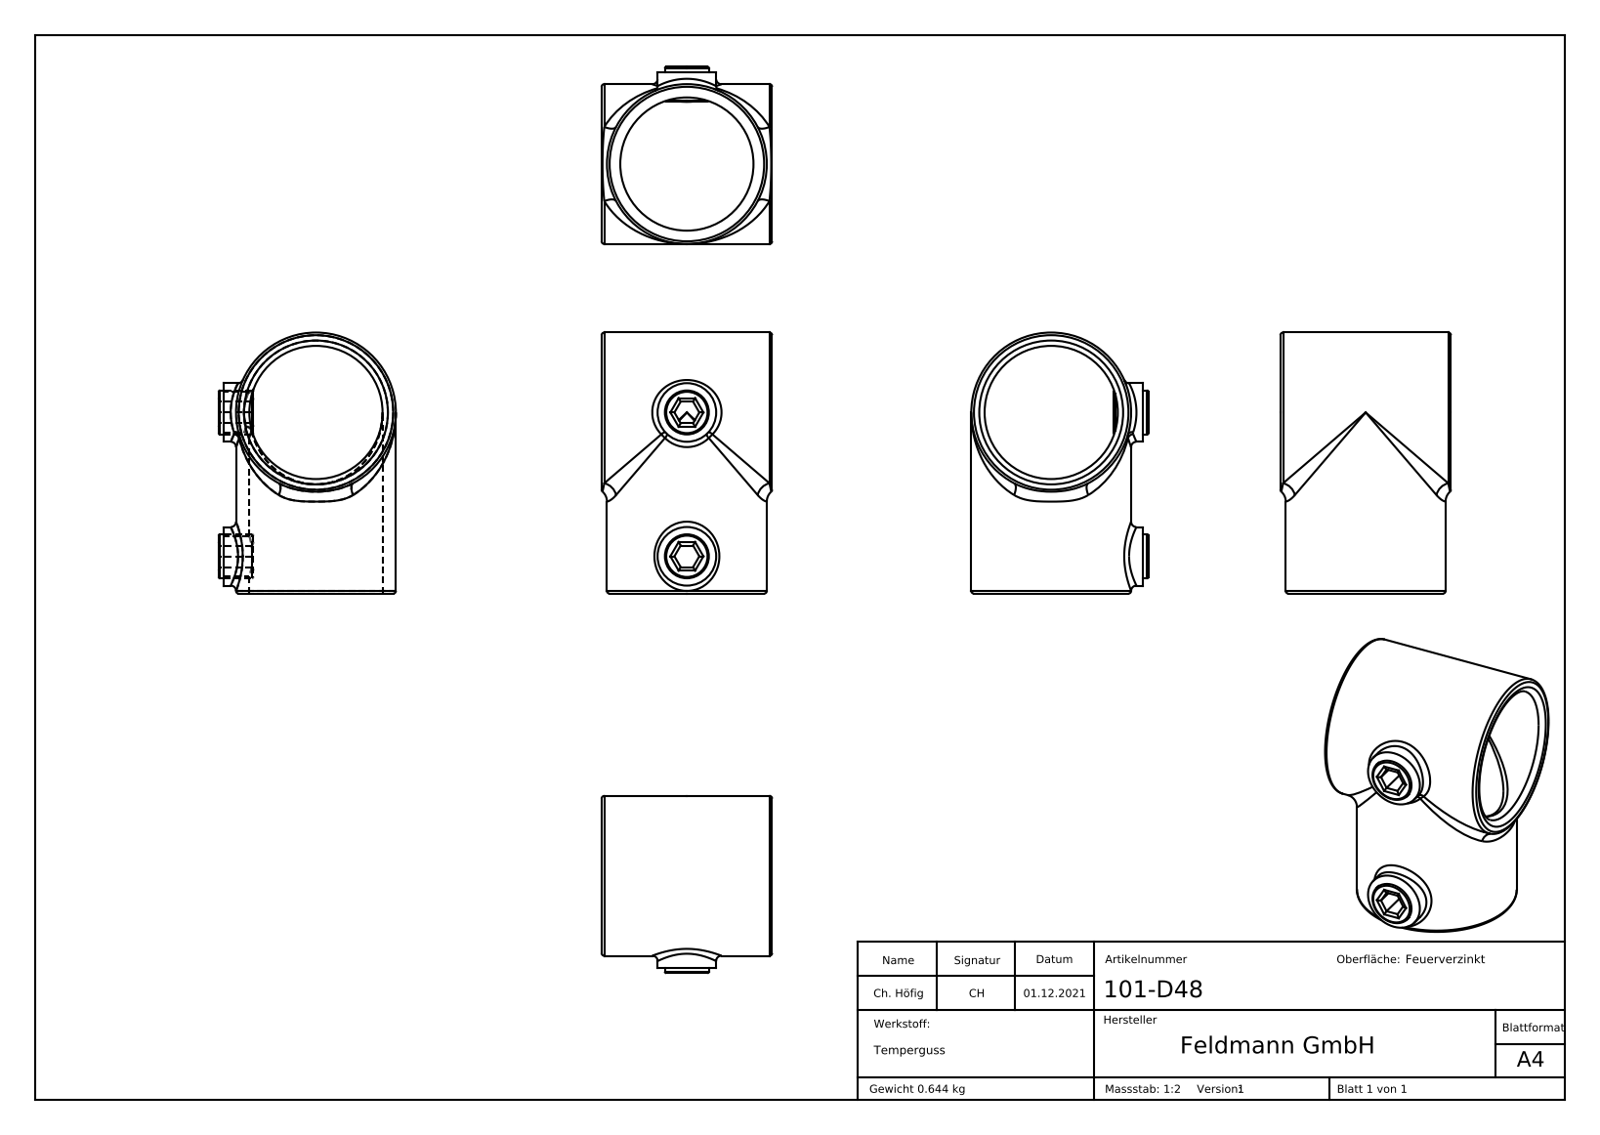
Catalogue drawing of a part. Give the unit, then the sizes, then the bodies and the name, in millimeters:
Units: millimetres
Overall size (bounding box): 98 × 66.5 × 64
Round holes (diameter × count): ⌀15.25 ×2, ⌀50 ×2
Round bosses / shafts (diameter × count): ⌀60 ×2, ⌀22 ×2, ⌀16.5 ×2
Partial cylindrical surfaces — rounded edges, fillets, slot ends (radius × count): R2 ×24
Main face-to-face distances: 64, 27, 8.1, 11, 13, 2, 54, 8.09, 9.95, 63.95
Hole centre spacings: 54
Volume: 87 830 mm³ · Surface area: 38 792 mm²
Bodies: 3 solids, 81 faces (21 planar, 34 cylindrical, 26 other)
Part name (STEP PRODUCT): 101-D48 Teil2; 101-D48 Teil1; 101-D48
STEP written by: SolidWorks 2018 (CONFIG_CONTROL_DESIGN)
